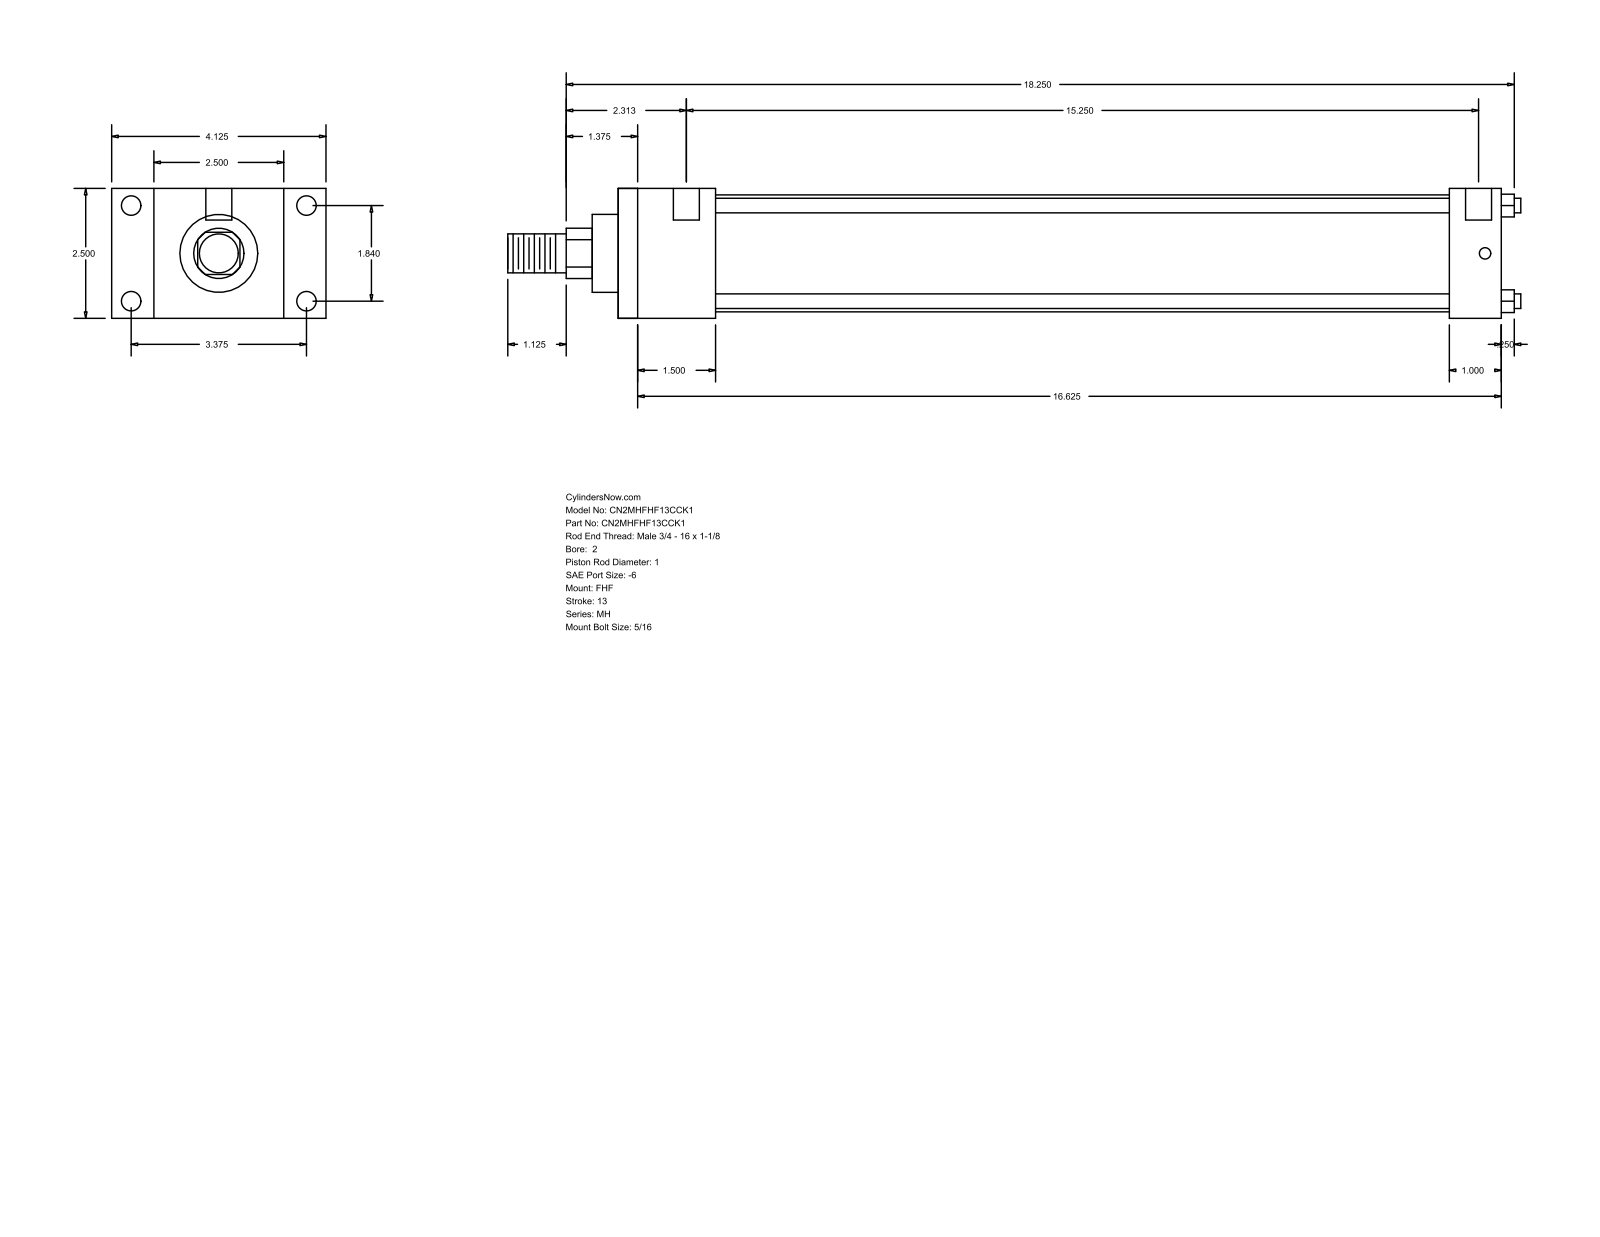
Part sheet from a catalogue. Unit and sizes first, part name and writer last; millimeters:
Units: millimetres
Overall size (bounding box): 495.3 × 104.78 × 63.5
Round holes (diameter × count): ⌀5.56 ×4, ⌀9.53 ×4, ⌀12.7 ×2
Round bosses / shafts (diameter × count): ⌀7.14 ×4, ⌀57.15 ×1, ⌀38.1 ×1, ⌀25.4 ×1, ⌀19.05 ×1
Partial cylindrical surfaces — rounded edges, fillets, slot ends (radius × count): R12.29 ×1
Main face-to-face distances: 63.5, 431.8, 47.63, 384.17, 20.64, 84.14, 104.78, 25.4, 406.4, 358.77
Hole centre spacings: 46.74, 85.72, 97.63, 395.28, 3.17, 4.76, 387.35, 390.52
Bodies: 0 solids, 88 faces (60 planar, 28 cylindrical, 0 other)
Part name (STEP PRODUCT): MH_FHF__0200_1
STEP written by: GSSL Pune (CONFIG_CONTROL_DESIGN)
